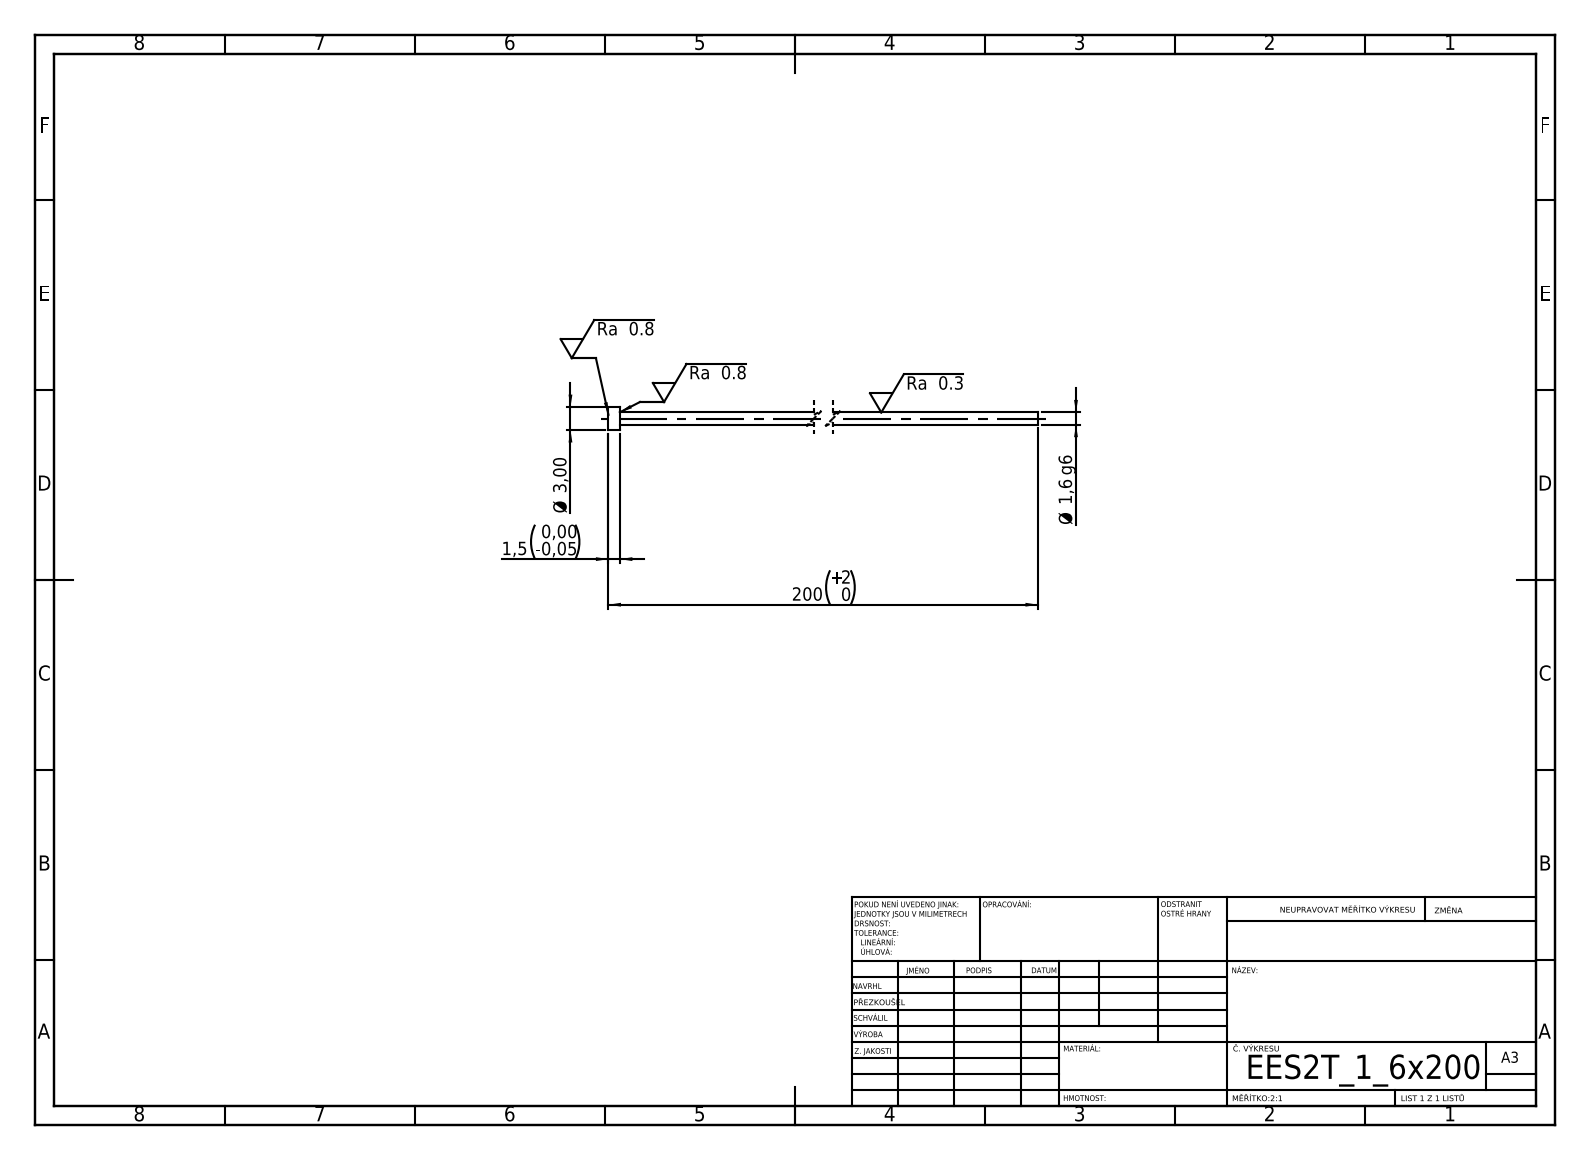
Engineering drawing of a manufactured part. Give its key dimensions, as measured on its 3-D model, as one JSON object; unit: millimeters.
{"step_written_by": "SolidWorks 2019 (CONFIG_CONTROL_DESIGN)", "units": "millimeters", "bodies": {"solids": 1, "faces": 7, "planar": 3, "cylindrical": 4, "other": 0}, "overall_size": [200, 3, 3], "volume_mm3": 410, "surface_area_mm2": 1026, "round_bosses_or_shafts": [[3, 1], [1.6, 1]], "face_to_face_distances": [1.5, 200, 198.5]}
